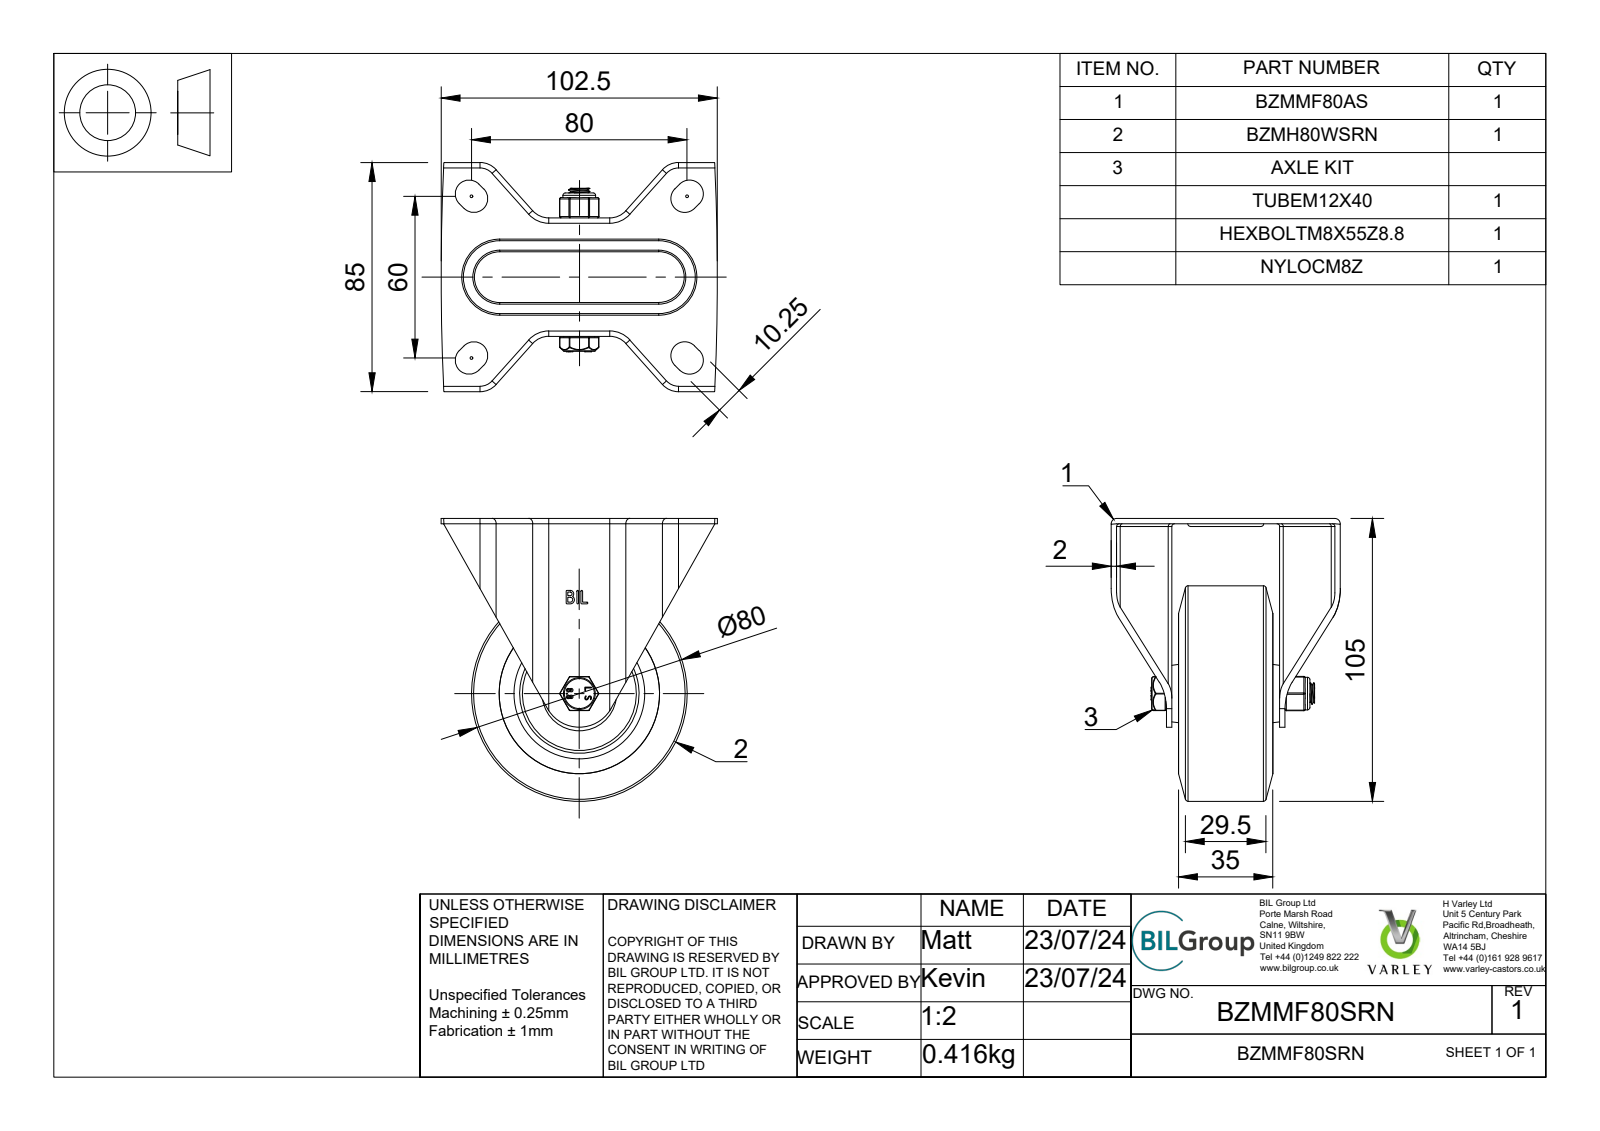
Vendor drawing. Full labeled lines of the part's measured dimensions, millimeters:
Part name (STEP PRODUCT): BZMMF80SRN v3; BZMMF80AS - 40 v2; ZINC PLATED, PRESSED STEEL BRACKET; BZMH80WSRN v1 (+8 more)
STEP written by: Autodesk Translation Framework v13.14.0.145 (AUTOMOTIVE_DESIGN)
Units: millimetres
Bodies: 7 solids, 389 faces (125 planar, 161 cylindrical, 103 other)
Overall size (bounding box): 105 × 102.5 × 85
Volume: 172 498 mm³ · Surface area: 77 471 mm²
Round holes (diameter × count): ⌀0.66 ×2, ⌀8 ×1, ⌀8.25 ×1, ⌀8.4 ×1, ⌀8.6 ×1, ⌀12.2 ×1, ⌀59.5 ×1
Round bosses / shafts (diameter × count): ⌀80 ×1, ⌀12.1 ×1, ⌀11.9 ×1, ⌀11.5 ×1, ⌀7.87 ×1, ⌀6.45 ×1
Partial cylindrical surfaces — rounded edges, fillets, slot ends (radius × count): R0.5 ×18, R0.25 ×12, R1 ×12, R2 ×8, R4 ×8, R5.12 ×8, R8 ×8, R0.33 ×4
Main face-to-face distances: 2, 5.16, 42, 40, 3.16, 7.16, 4.5, 39.5, 2.5, 37.5
Hole centre spacings: 3.22, 2.49
